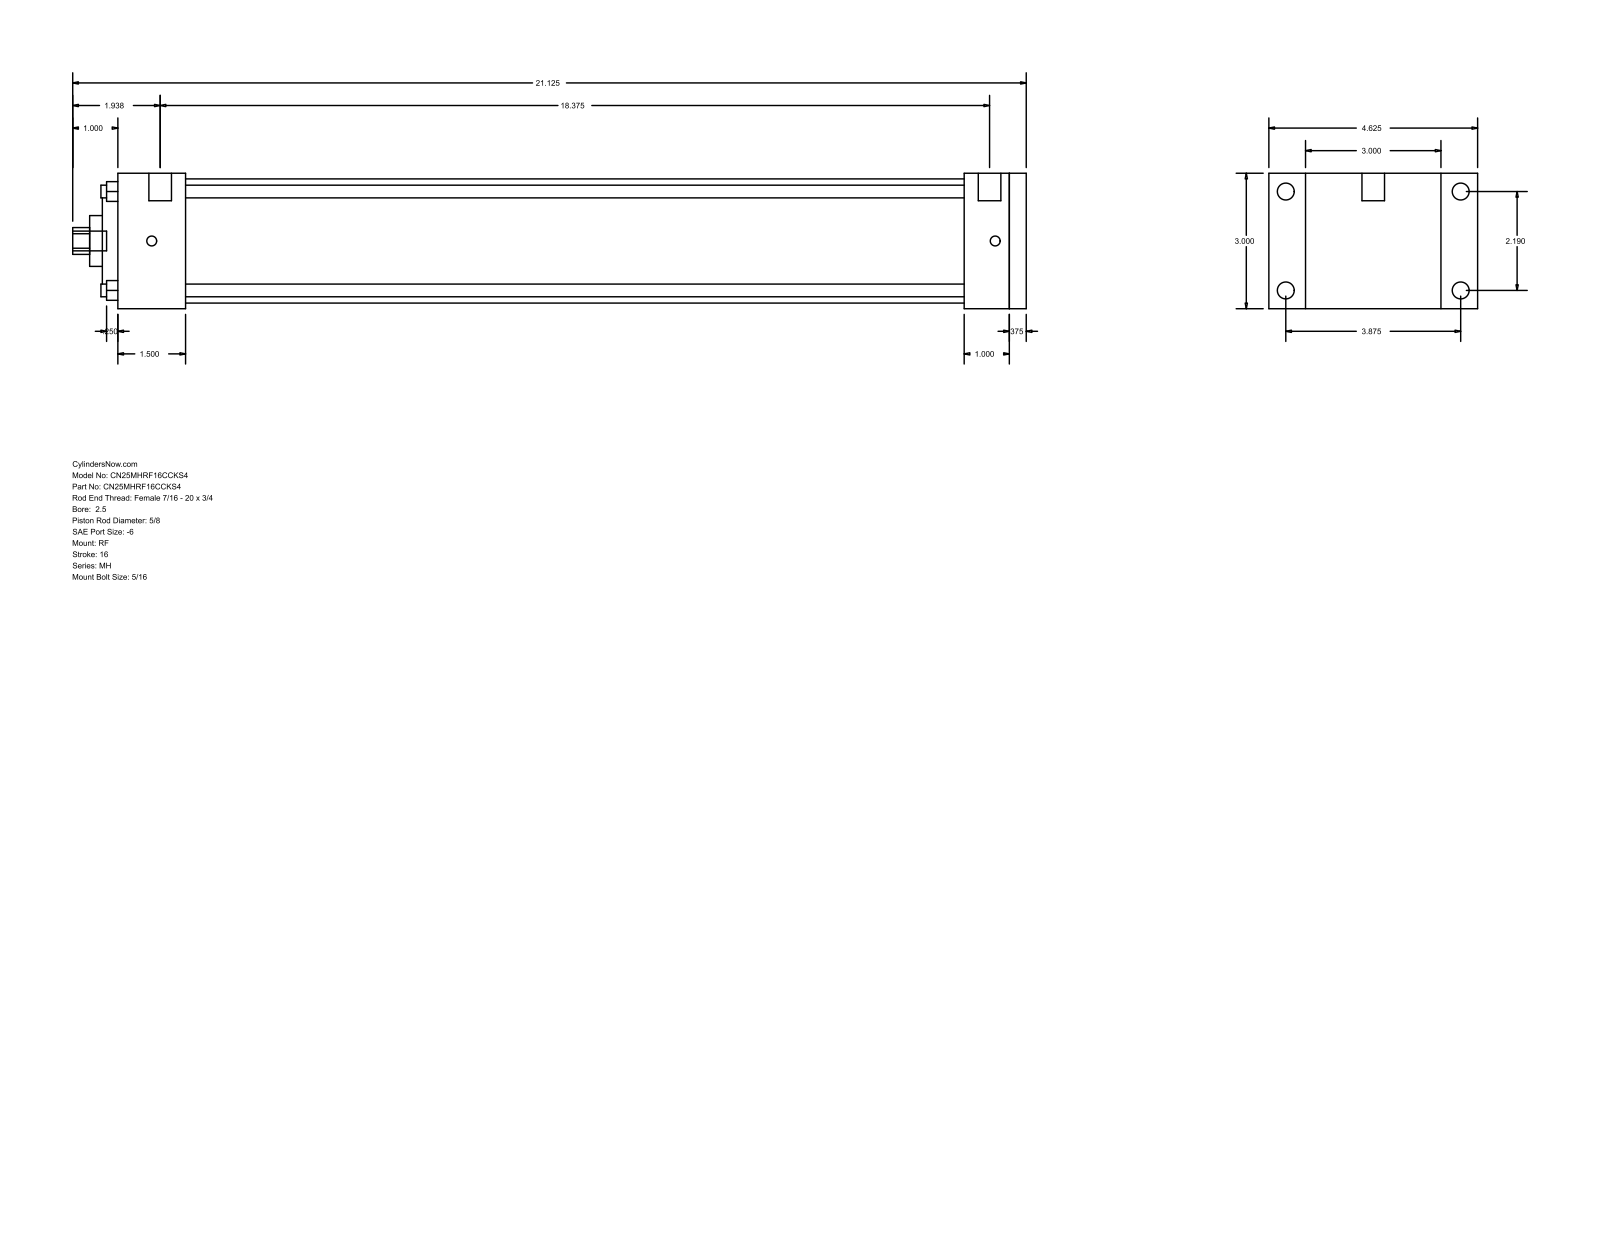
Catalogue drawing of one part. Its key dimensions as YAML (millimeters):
part_name: "MH_RF__0250_0.625"
step_written_by: "GSSL Pune (CONFIG_CONTROL_DESIGN)"
units: millimeters
bodies: {solids: 0, faces: 94, planar: 65, cylindrical: 29, other: 0}
overall_size: [536.58, 117.47, 76.2]
round_holes:
  - {diameter: 7.14, count: 4}
  - {diameter: 15.88, count: 1}
  - {diameter: 28.57, count: 1}
  - {diameter: 55.55, count: 1}
  - {diameter: 69.85, count: 1}
round_bosses_or_shafts:
  - {diameter: 9.53, count: 4}
  - {diameter: 5.56, count: 4}
  - {diameter: 12.7, count: 2}
  - {diameter: 11.11, count: 1}
partial_cylinders:
  - {radius: 7.54, count: 1}
face_to_face_distances: [76.2, 9.53, 511.18, 501.65, 25.4, 476.25, 34.93, 38.1, 438.15, 463.55]
hole_center_spacings: [39.33, 55.62, 78.66]
